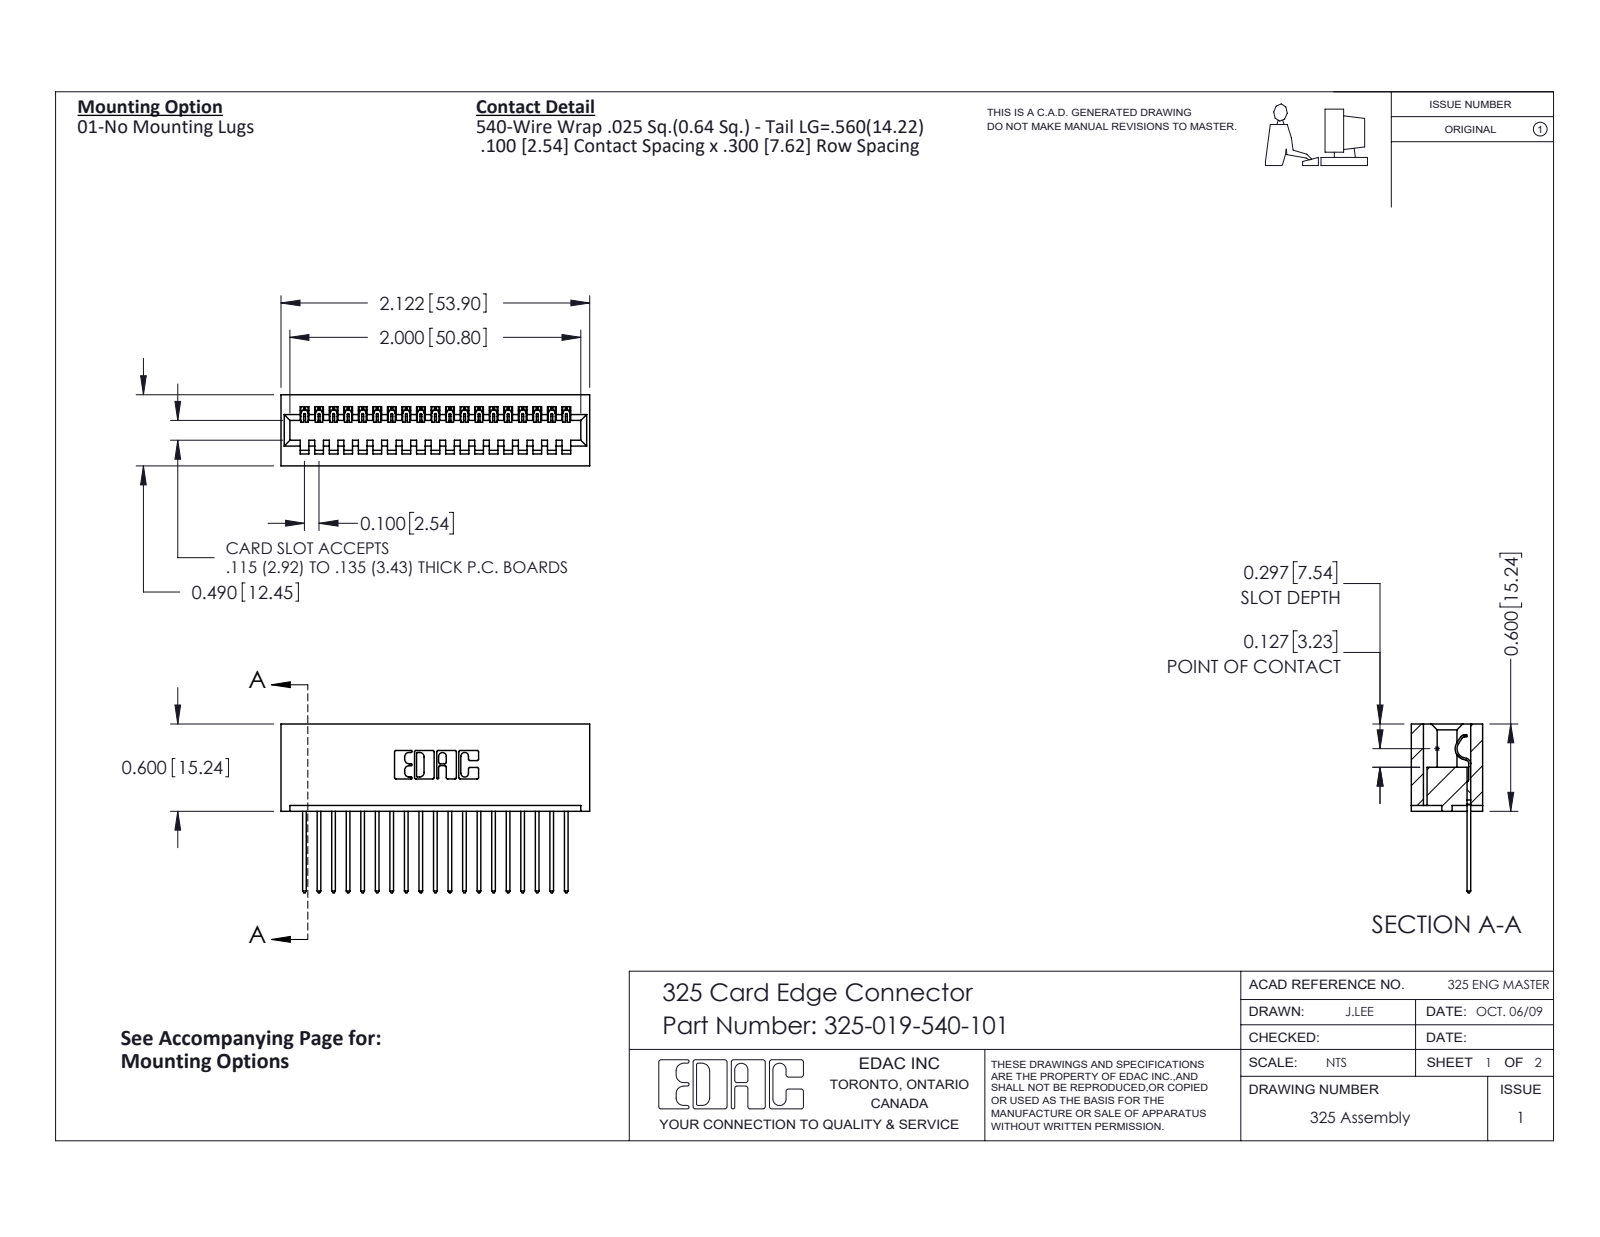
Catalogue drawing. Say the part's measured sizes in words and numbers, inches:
The part is named "325 Part_Lugless; 325-292-001_325-293-140; 325-019-540-101". Its 3-D file was written by "SolidWorks 2016 (CONFIG_CONTROL_DESIGN)". It is 20 solids with 1208 faces: 864 planar, 344 cylindrical and 0 other. Overall it measures 2.122 by 1.16 by 0.49 inches. Its volume is 0.443 cubic inches and its surface area 12.74 square inches. Partial cylindrical surfaces (rounded edges, fillets, slot ends): 38 of radius 0.006, 38 of radius 0.01, 22 of radius 0.01, 6 of radius 0.007, 6 of radius 0.031, 3 of radius 0.026, 1 of radius 0.014, 1 of radius 0.022. The main face-to-face distances are 0.083, 0.407, 0.3, 0.49, 0.107, 0.383, 0.025, 0.1, 0.2, 0.56.
